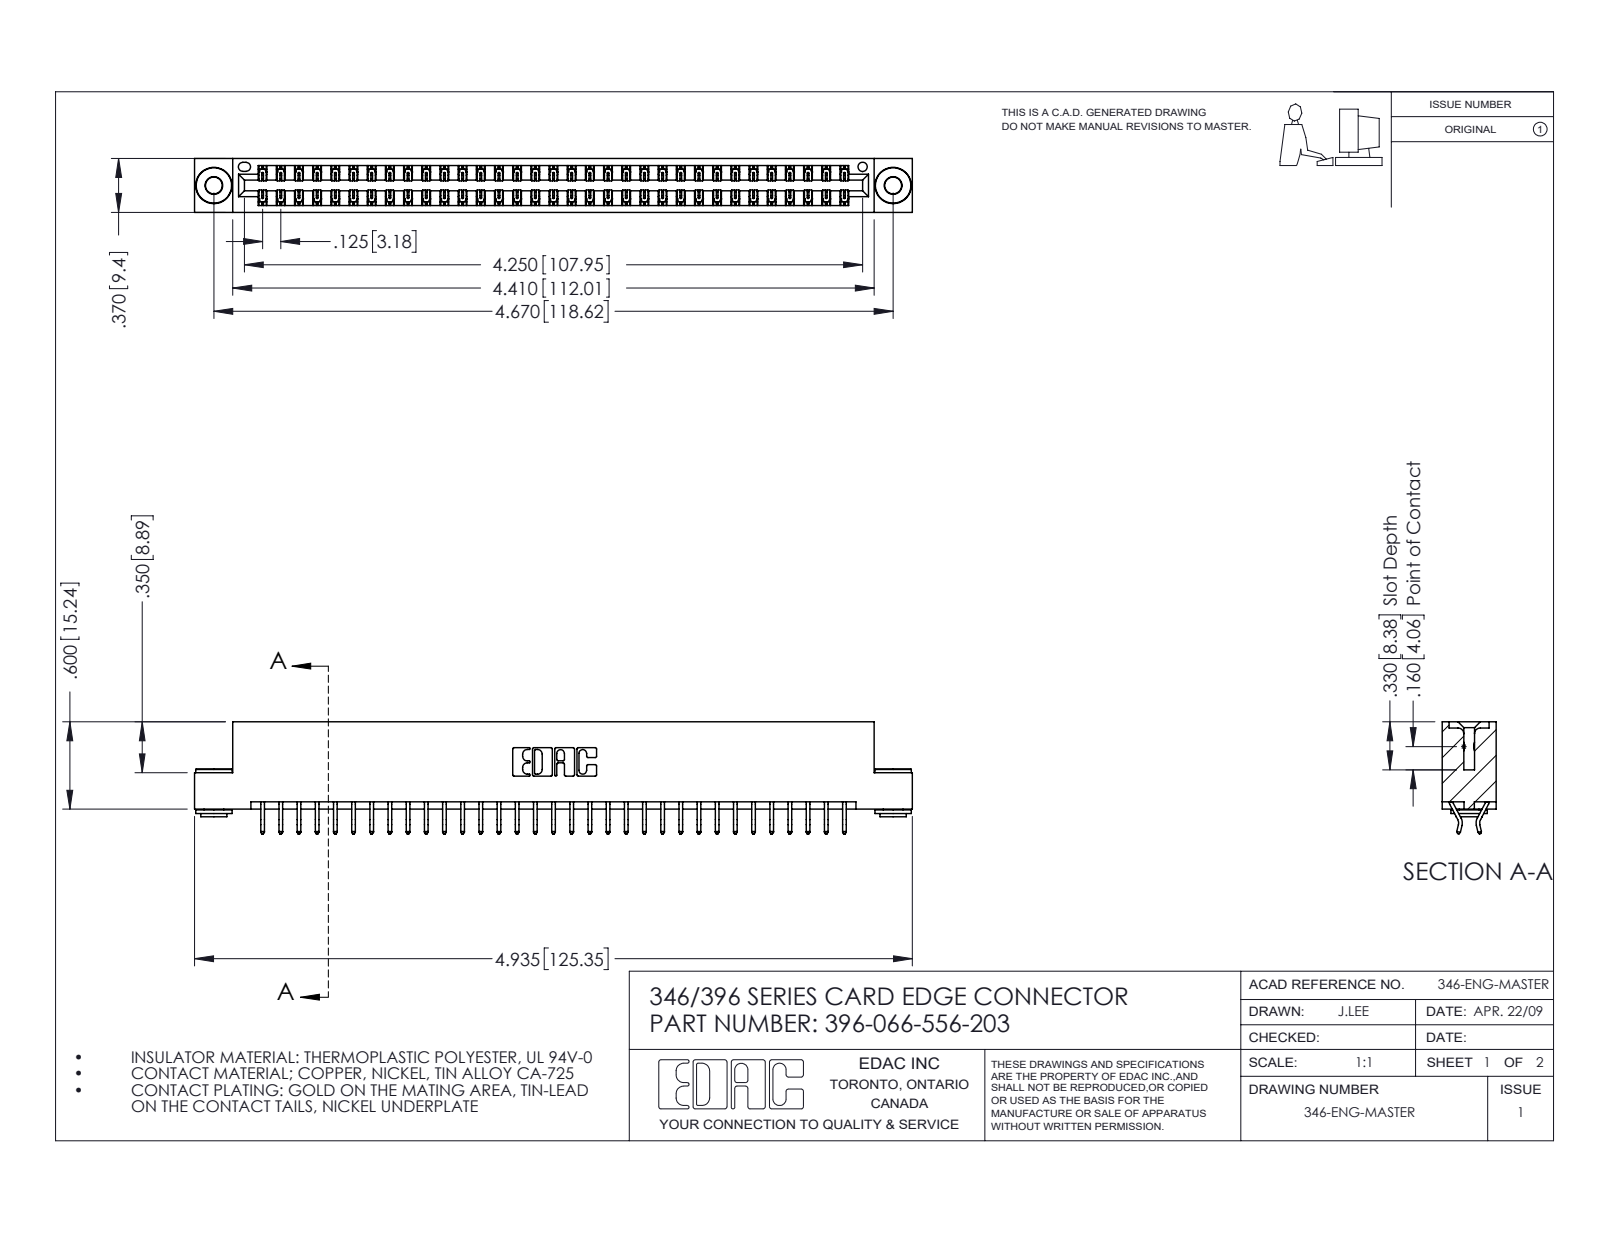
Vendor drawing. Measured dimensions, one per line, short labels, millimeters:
name: 345-292-001_556 Tail; 396-066-556-203; 346 Part_Flush Mounting Lugs - 0.156 Dia-TH; 345-250-002_345-250-002-102
written by: SolidWorks 2016 (CONFIG_CONTROL_DESIGN)
unit: mm
bodies: 69 solids, 3988 faces (2660 planar, 1320 cylindrical, 8 other)
size: 125.3 × 19.6 × 9.4
volume: 12 200 mm³; area: 16 740 mm²
holes: 2× ⌀2.9, 2× ⌀4, 1× ⌀1.6
bosses: 2× ⌀6.4, 2× ⌀4.6, 2× ⌀3.5
rounds: 99× R0.2, 22× R0.3, 6× R0.2, 6× R0.8, 3× R0.7, 2× R0.3, 2× R0.4, 2× R0.6
face distances: 1.2, 8.2, 9.4, 6.4, 0.6, 1.8, 7.6, 7, 3.8, 5.6
hole spacings: 6.2, 113.3, 118.6
